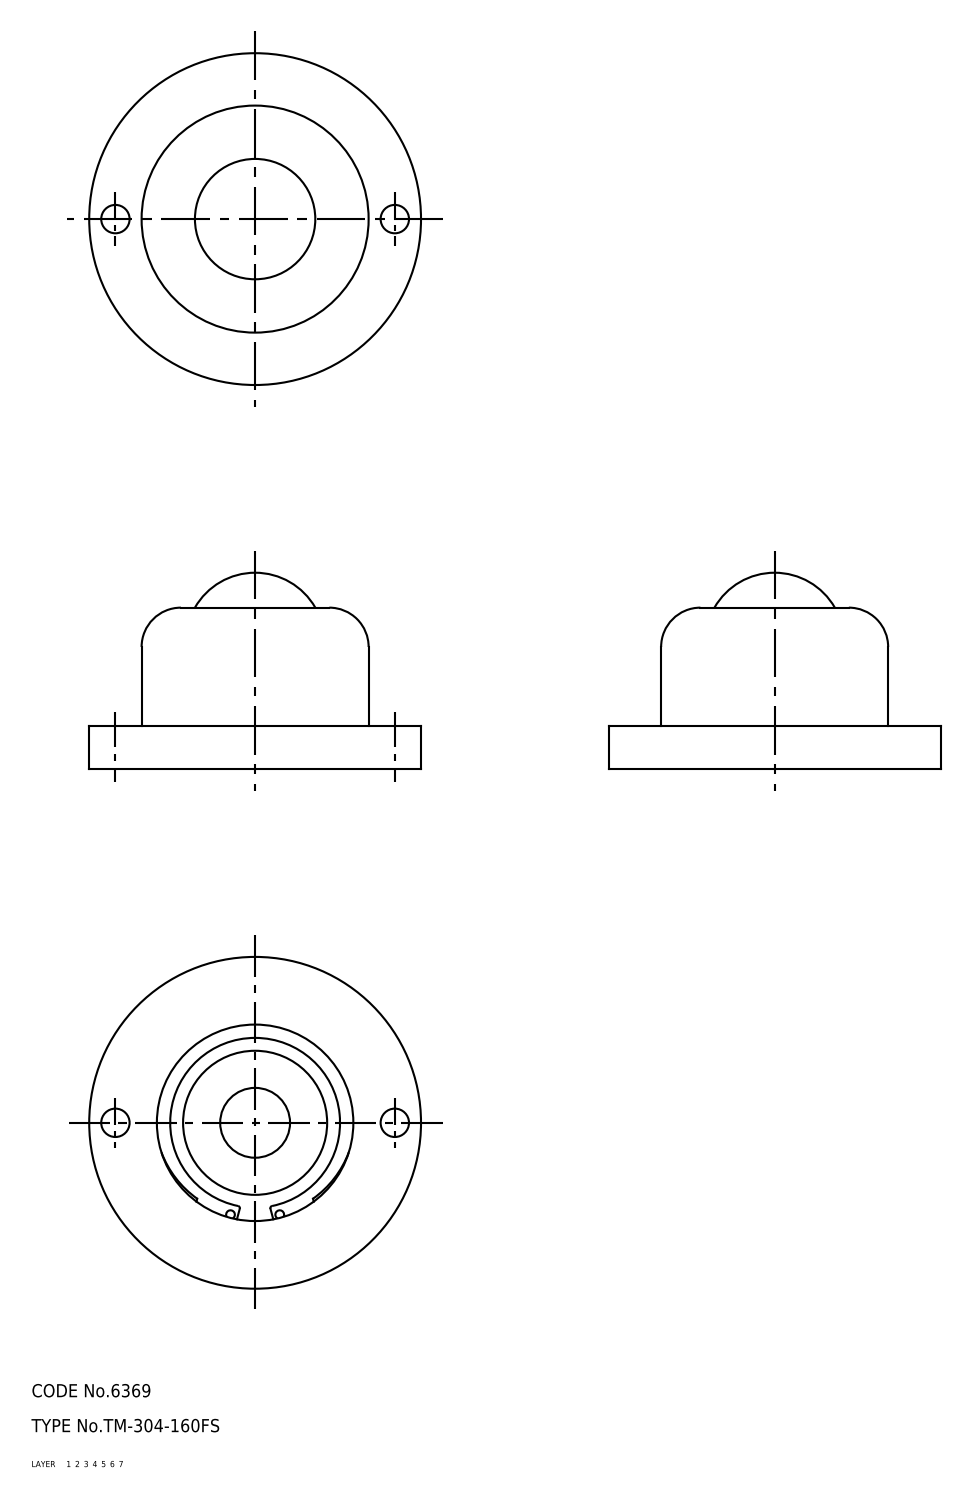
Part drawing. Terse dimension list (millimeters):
name: 67112631; 67112644
written by: CADfix (AUTOMOTIVE_DESIGN)
unit: mm
bodies: 2 solids, 52 faces (0 planar, 0 cylindrical, 52 other)
size: 76 × 76 × 45
volume: 62 015 mm³; area: 26 353 mm²
